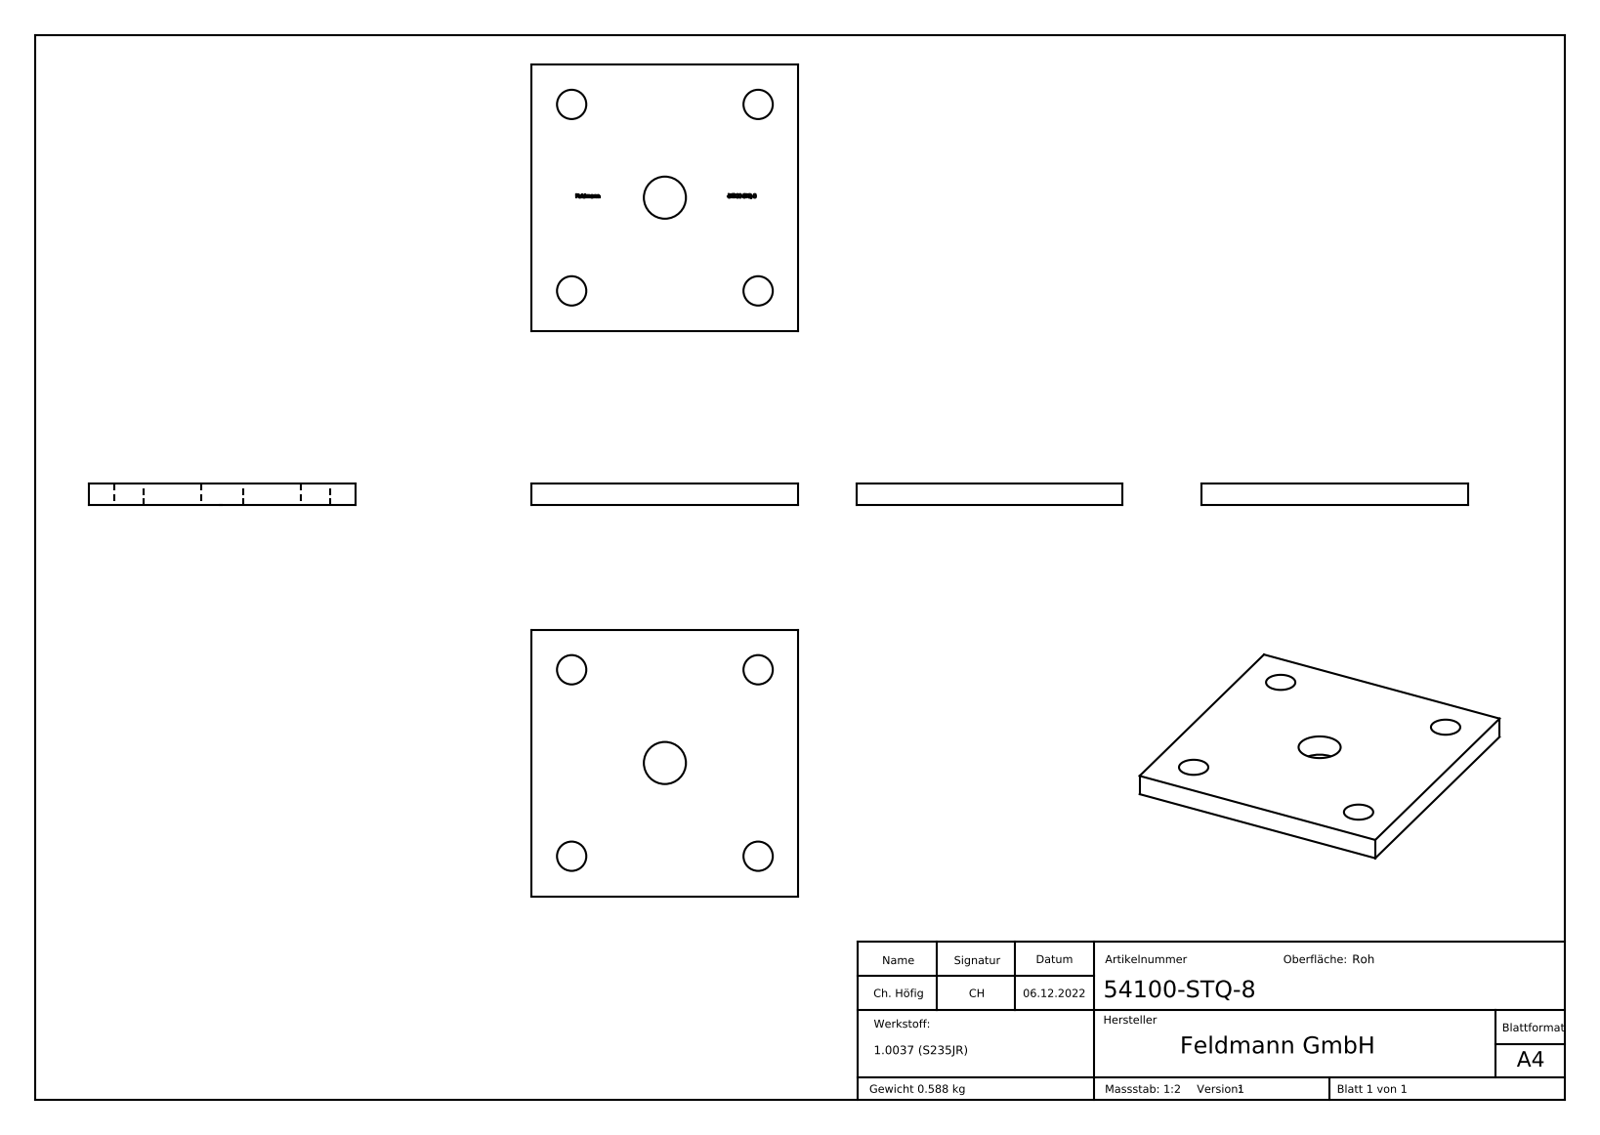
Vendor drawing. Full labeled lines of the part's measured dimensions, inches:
Part name (STEP PRODUCT): 54100-STQ-8
STEP written by: SolidWorks 2018 (CONFIG_CONTROL_DESIGN)
Units: inches
Bodies: 1 solid, 258 faces (137 planar, 5 cylindrical, 116 other)
Overall size (bounding box): 3.937 × 3.937 × 0.315
Volume: 4.601 in³ · Surface area: 36.52 in²
Round holes (diameter × count): ⌀0.433 ×4, ⌀0.622 ×1
Main face-to-face distances: 0.315, 3.937, 0.311, 1.969, 0.035, 0.174, 2.338, 2.512, 0.052, 2.02
Hole centre spacings: 1.949, 2.756, 3.897
